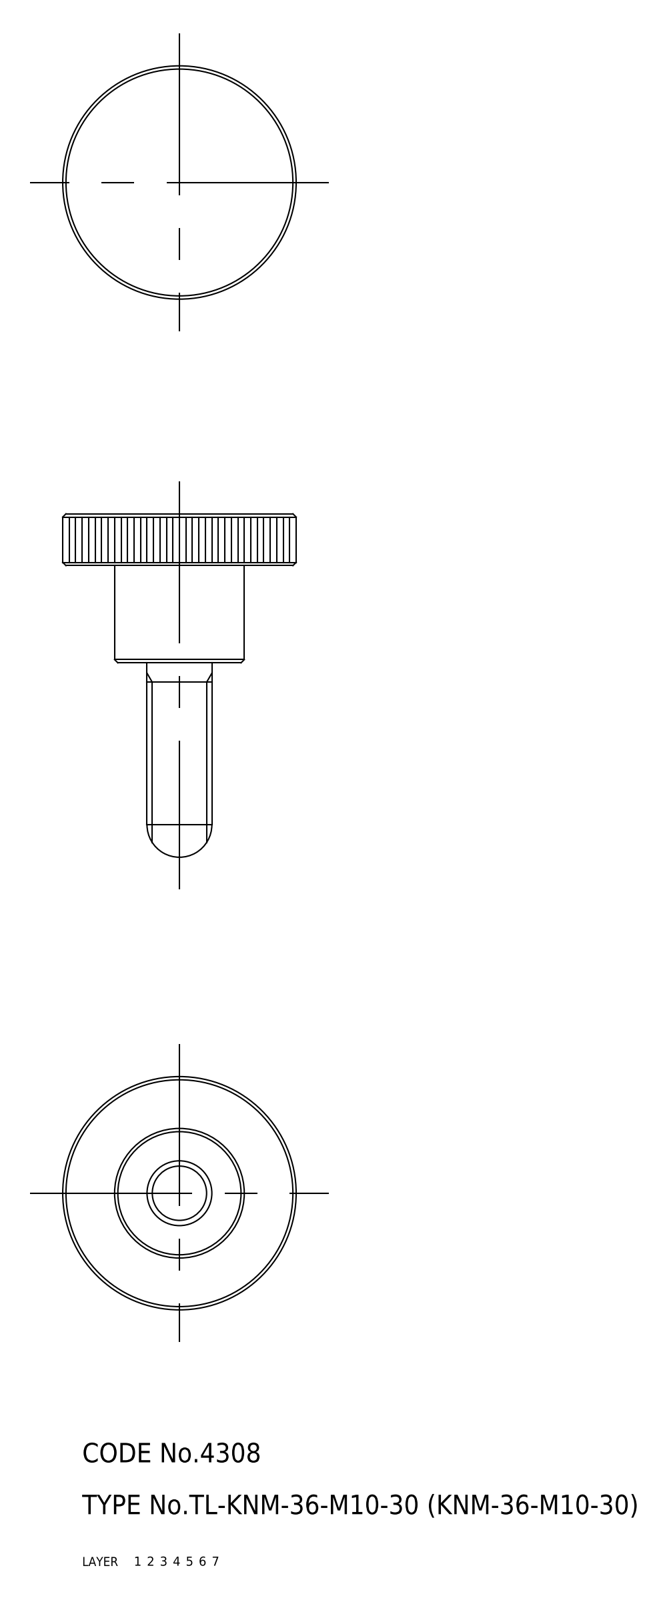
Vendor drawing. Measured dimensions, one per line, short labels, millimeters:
name: knob
written by: CADfix (AUTOMOTIVE_DESIGN)
unit: mm
bodies: 1 solid, 16 faces (0 planar, 0 cylindrical, 16 other)
size: 53 × 36 × 36
volume: 15 071 mm³; area: 4 663 mm²
